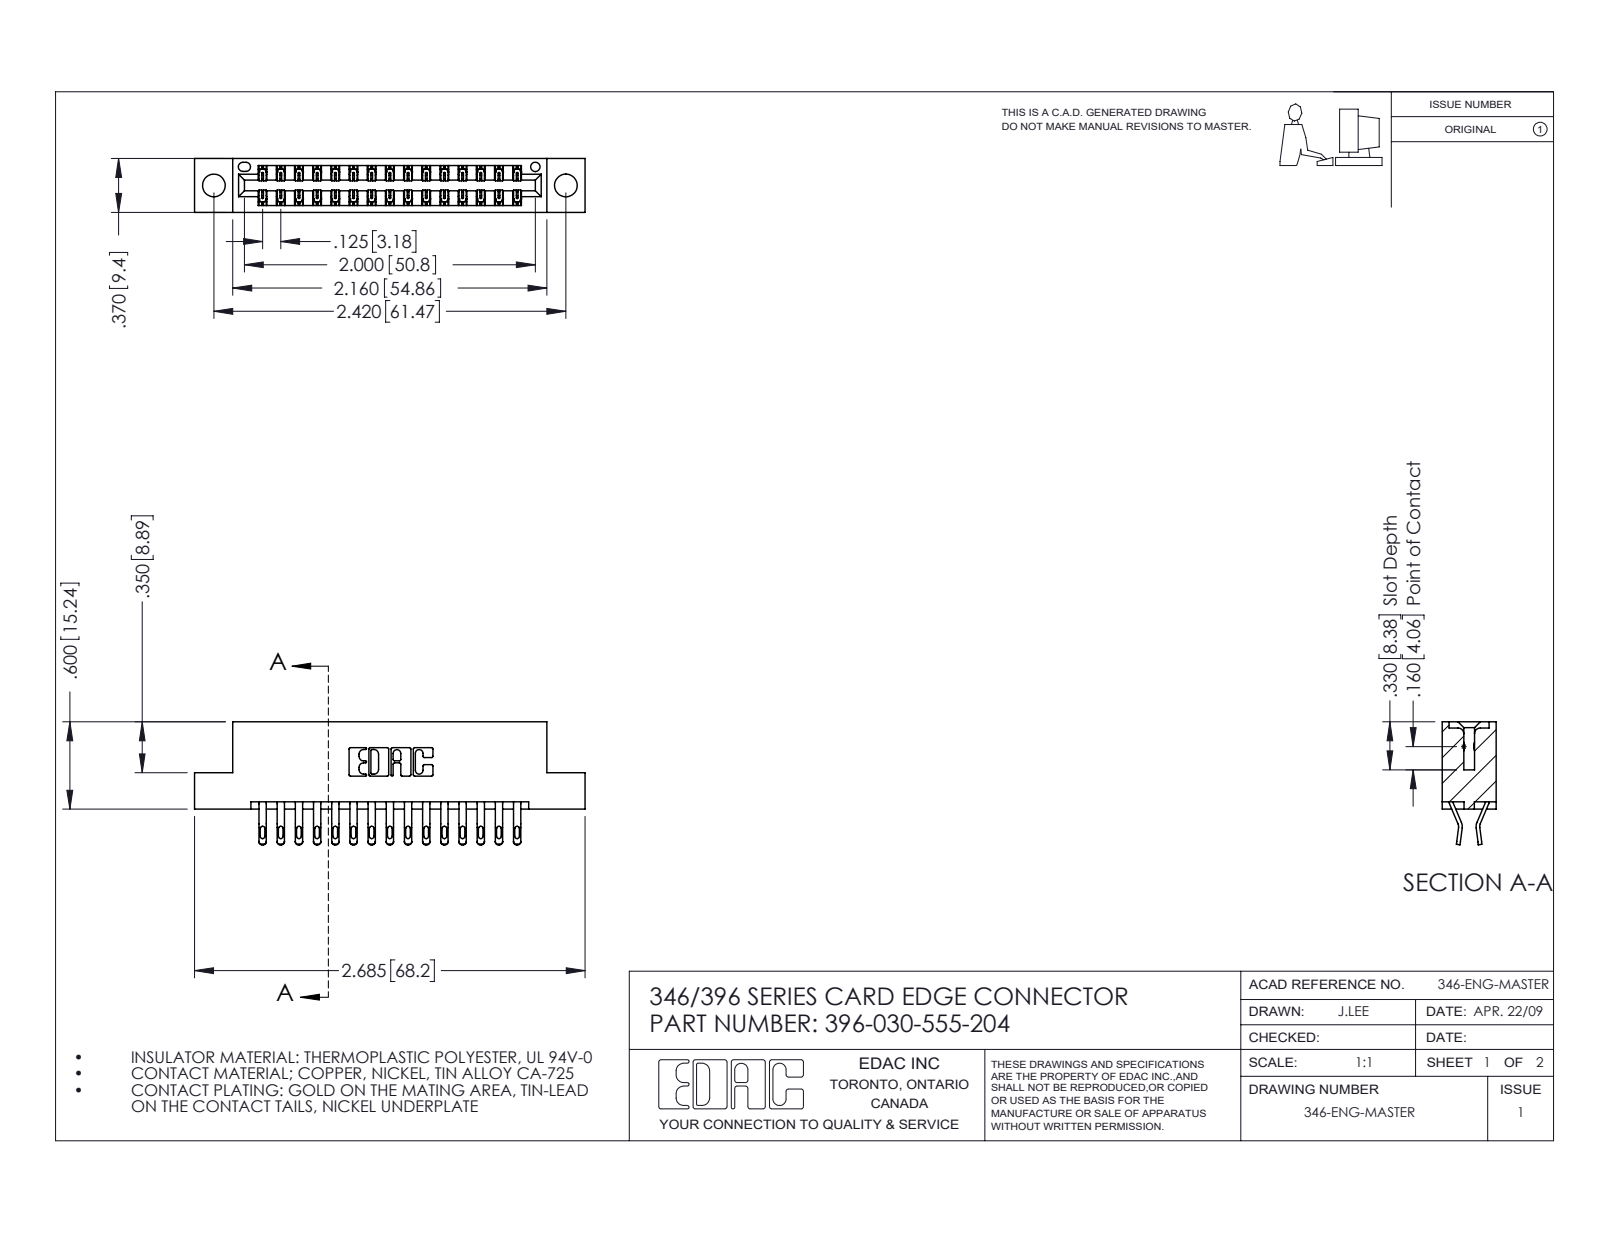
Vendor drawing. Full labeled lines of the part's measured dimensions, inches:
Part name (STEP PRODUCT): 346 Part_Flush Mounting Lugs - 0.156 Dia-TH; 345-292-001_555 Tail; 396-030-555-204
STEP written by: SolidWorks 2016 (CONFIG_CONTROL_DESIGN)
Units: inches
Bodies: 31 solids, 1862 faces (1066 planar, 796 cylindrical, 0 other)
Overall size (bounding box): 2.685 × 0.845 × 0.37
Volume: 0.393 in³ · Surface area: 13.25 in²
Round holes (diameter × count): ⌀0.156 ×2, ⌀0.064 ×1
Partial cylindrical surfaces — rounded edges, fillets, slot ends (radius × count): R0.016 ×60, R0.02 ×60, R0.006 ×45, R0.01 ×22, R0.007 ×6, R0.031 ×6, R0.026 ×3, R0.01 ×2
Main face-to-face distances: 0.048, 0.322, 0.25, 0.37, 0.025, 0.072, 0.298, 0.275, 0.148, 0.222
Hole centre spacings: 0.246, 2.213, 2.42
